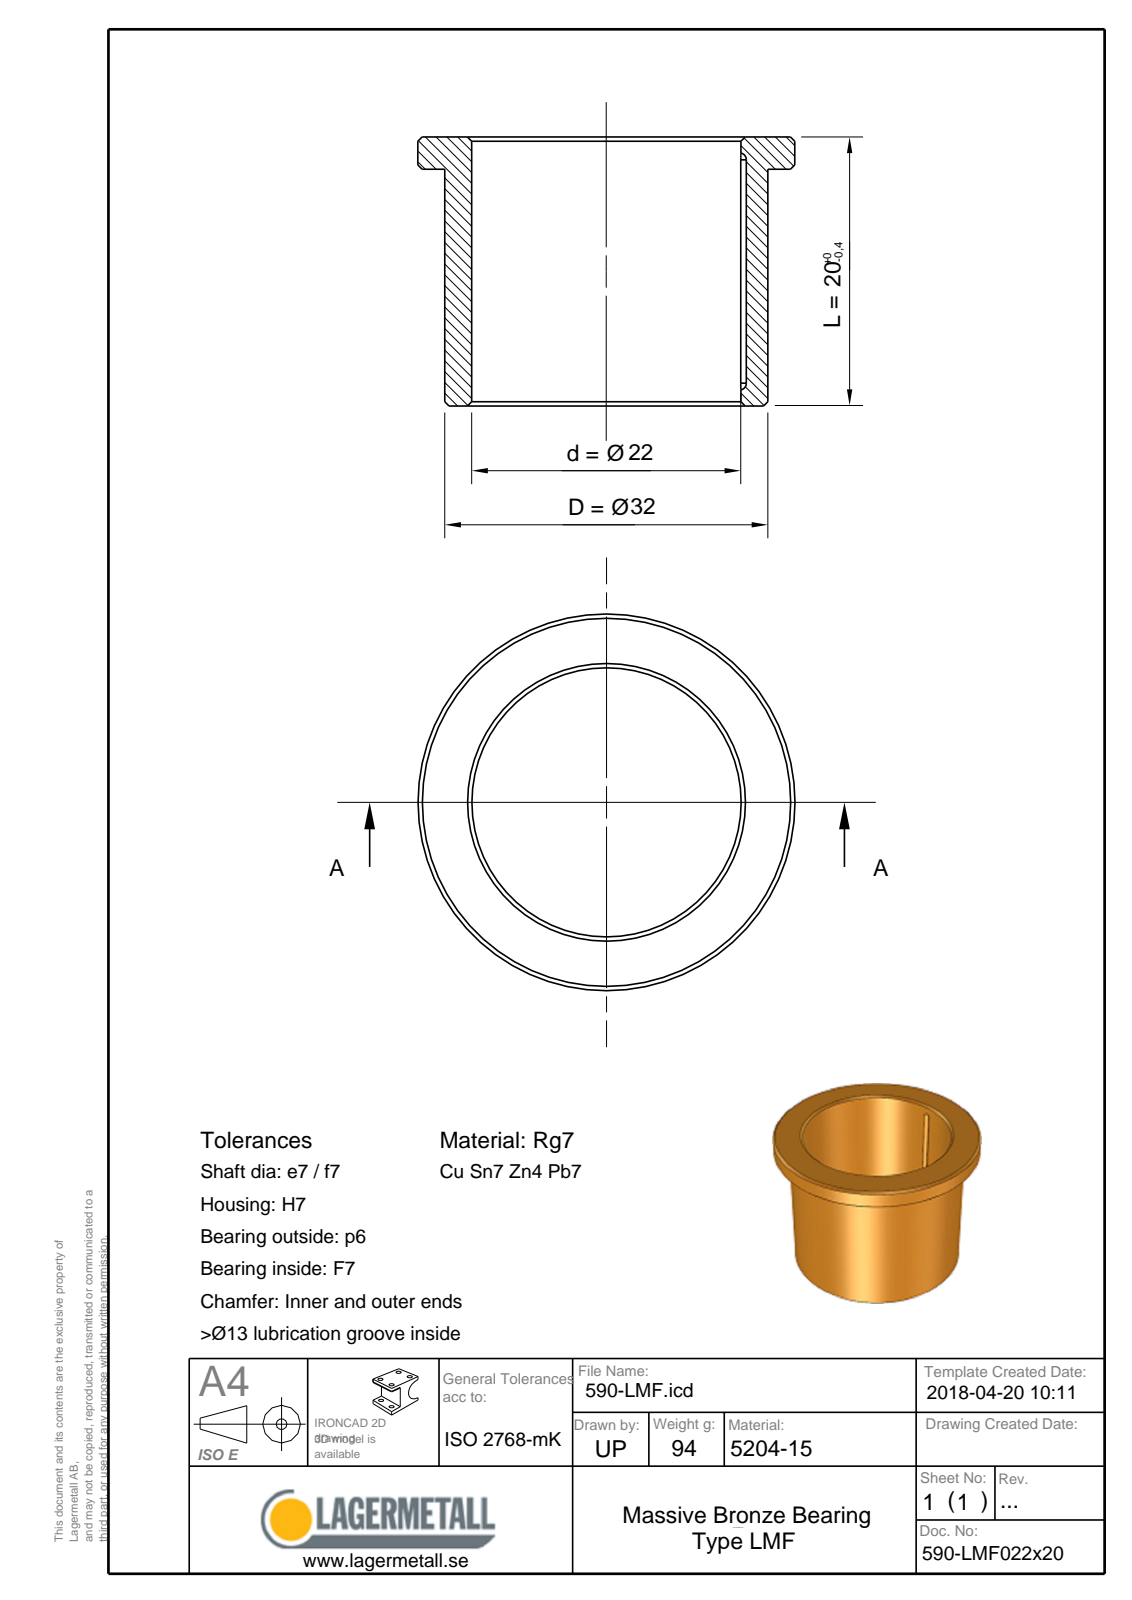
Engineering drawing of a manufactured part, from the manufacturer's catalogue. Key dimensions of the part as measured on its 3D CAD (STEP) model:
Part name (STEP PRODUCT): 590-LMF022x20
STEP written by: Spatial InterOp 3D (CONFIG_CONTROL_DESIGN)
Units: millimetres
Bodies: 1 solid, 18 faces (5 planar, 6 cylindrical, 7 other)
Overall size (bounding box): 40 × 40 × 20
Volume: 10 666 mm³ · Surface area: 5 148 mm²
Round holes (diameter × count): ⌀22 ×1
Round bosses / shafts (diameter × count): ⌀40 ×1, ⌀32 ×1
Partial cylindrical surfaces — rounded edges, fillets, slot ends (radius × count): R0.75 ×3
Main face-to-face distances: 5, 15, 20, 1.5
